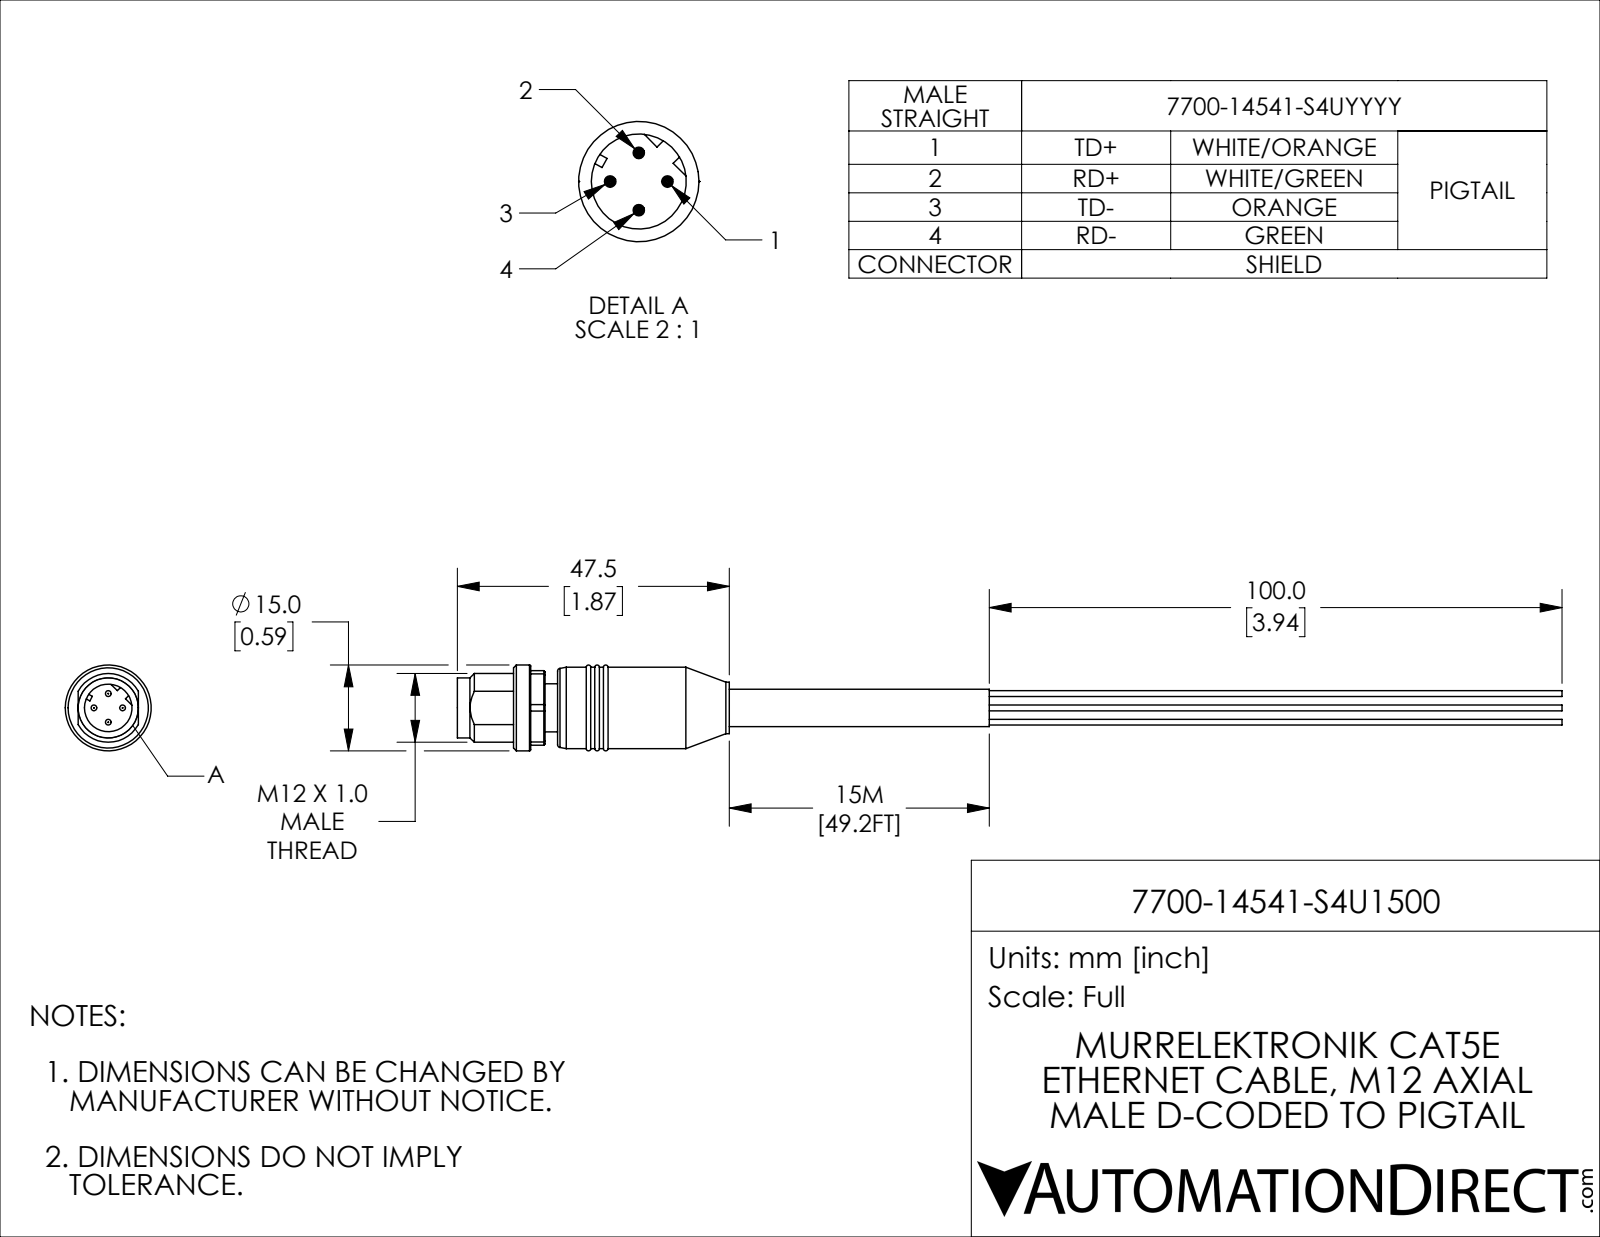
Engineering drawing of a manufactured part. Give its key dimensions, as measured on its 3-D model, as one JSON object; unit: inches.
{"part_name": "7700-14541-S4U1500", "step_written_by": "SolidWorks 2021 (CONFIG_CONTROL_DESIGN)", "units": "inches", "bodies": {"solids": 1, "faces": 125, "planar": 40, "cylindrical": 45, "other": 40}, "overall_size": [7.594, 0.591, 0.591], "volume_in3": 0.473, "surface_area_in2": 7.675, "round_holes": [[0.327, 1]], "round_bosses_or_shafts": [[0.039, 4], [0.591, 1], [0.559, 1], [0.413, 1], [0.354, 1], [0.331, 1], [0.256, 1]], "partial_cylinders_radius": [[0.236, 1], [0.283, 1]], "face_to_face_distances": [0.087, 0.035, 0.252, 0.339, 0.217, 0.303, 0.512, 0.413, 0.35, 0.386]}
